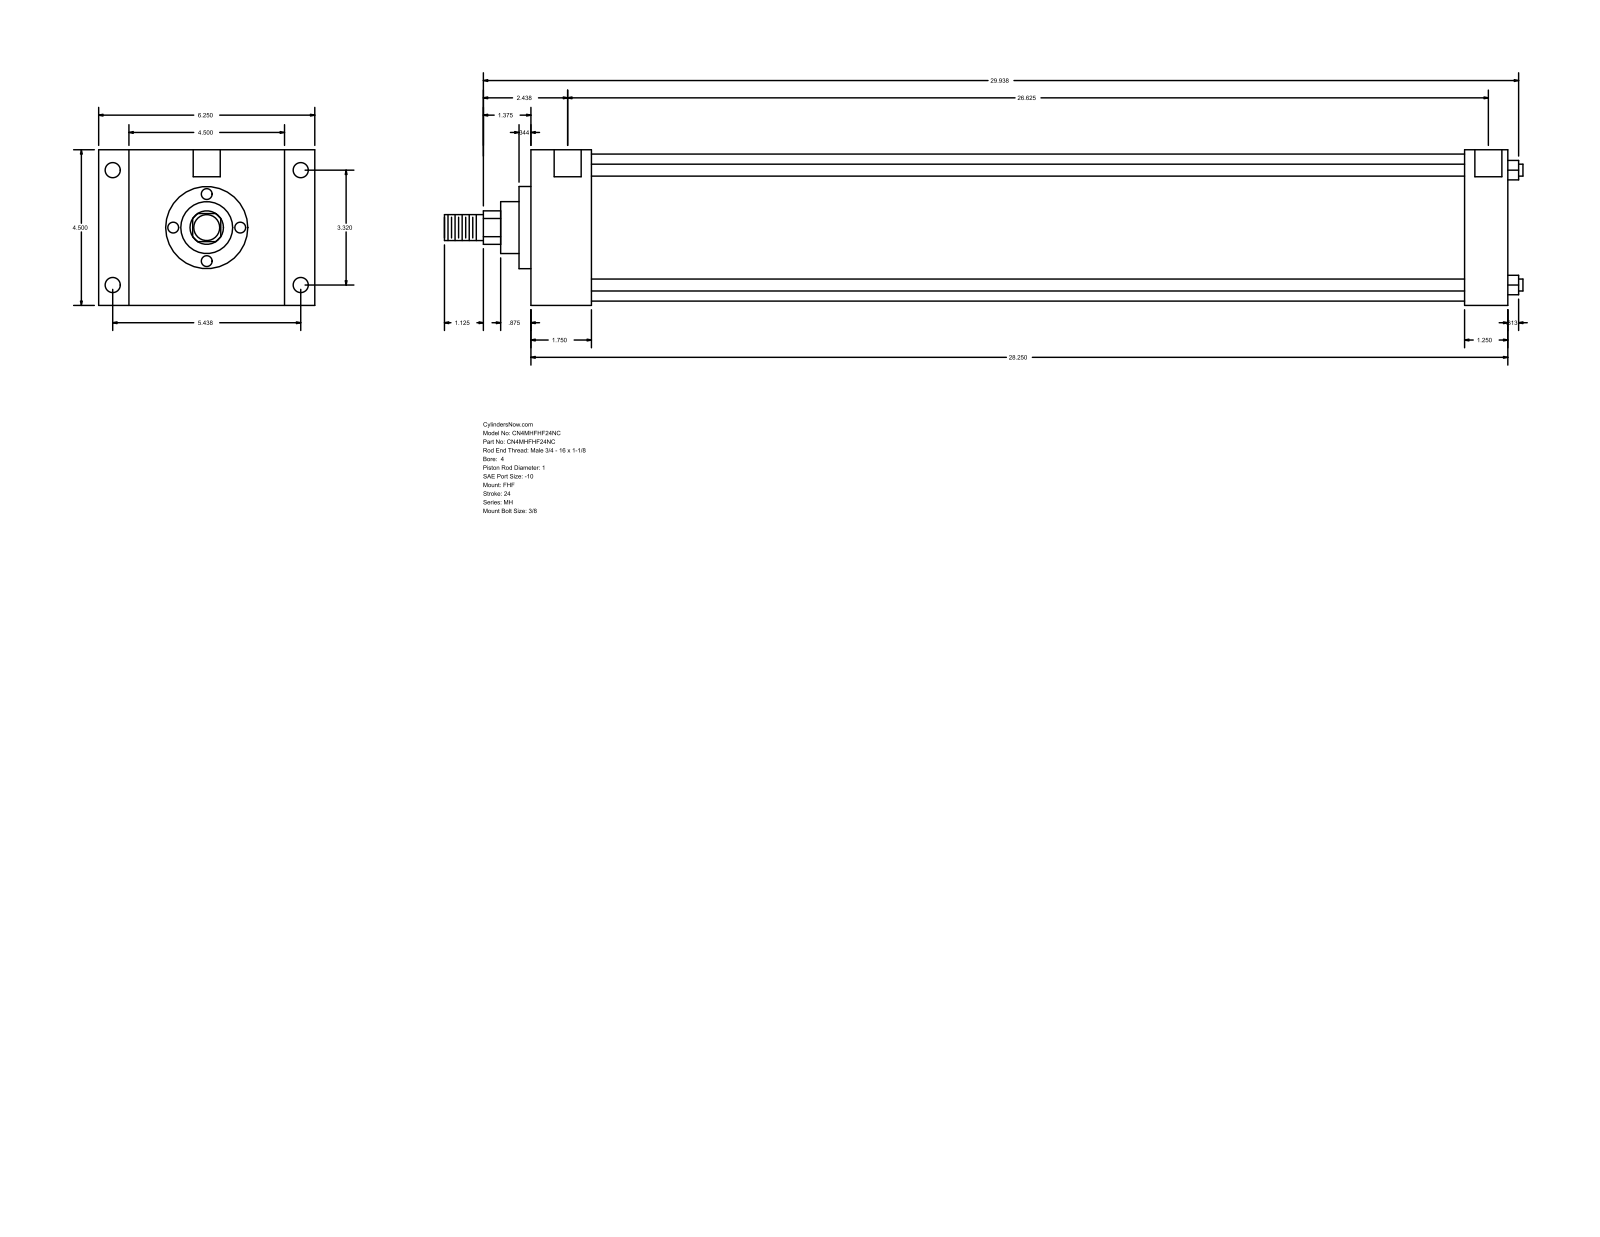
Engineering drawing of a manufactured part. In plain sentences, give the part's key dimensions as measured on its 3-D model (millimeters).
The part is named "MH_FHF__0400_1". Its 3-D file was written by "GSSL Pune (CONFIG_CONTROL_DESIGN)". It is 0 solids with 90 faces: 61 planar, 29 cylindrical and 0 other. Overall it measures 792.16 by 158.75 by 114.3 millimeters. Round holes: 4 of diameter 8.73, 4 of diameter 11.13, 2 of diameter 19.84. Round bosses or shafts: 4 of diameter 8.76, 1 of diameter 107.95, 1 of diameter 60.33, 1 of diameter 38.1, 1 of diameter 25.4, 1 of diameter 19.05. Partial cylindrical surfaces (rounded edges, fillets, slot ends): 1 of radius 12.29. The main face-to-face distances are 114.3, 717.56, 44.46, 673.1, 22.23, 136.53, 158.76, 685.81, 641.35, 31.75. The hole center spacings are 1.58, 84.32, 138.12, 161.82, 677.86, 679.44, 676.28.
